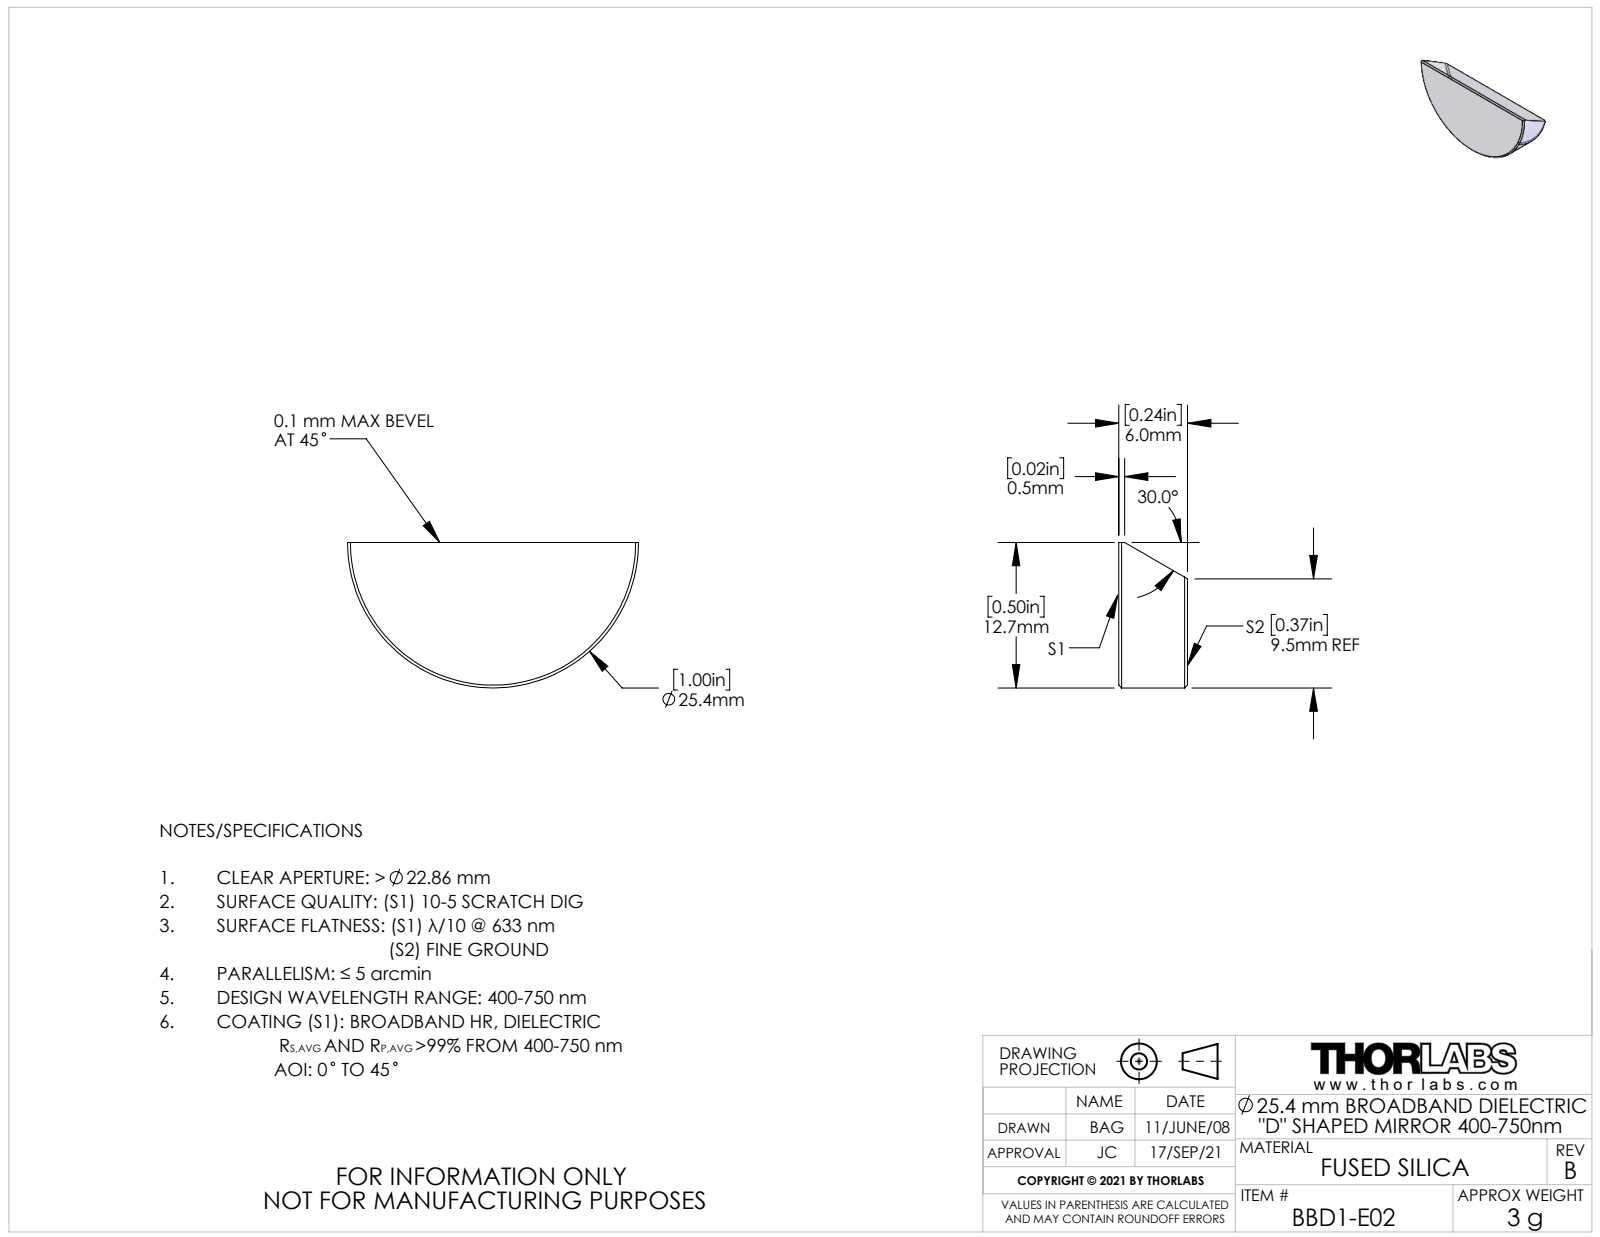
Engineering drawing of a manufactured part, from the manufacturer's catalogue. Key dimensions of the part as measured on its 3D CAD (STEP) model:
Part name (STEP PRODUCT): 18304-E0W
STEP written by: SolidWorks 2007 (AUTOMOTIVE_DESIGN)
Units: inches
Bodies: 1 solid, 8 faces (5 planar, 1 cylindrical, 2 other)
Overall size (bounding box): 1 × 0.5 × 0.236
Volume: 0.079 in³ · Surface area: 1.255 in²
Partial cylindrical surfaces — rounded edges, fillets, slot ends (radius × count): R0.5 ×1
Main face-to-face distances: 0.236
